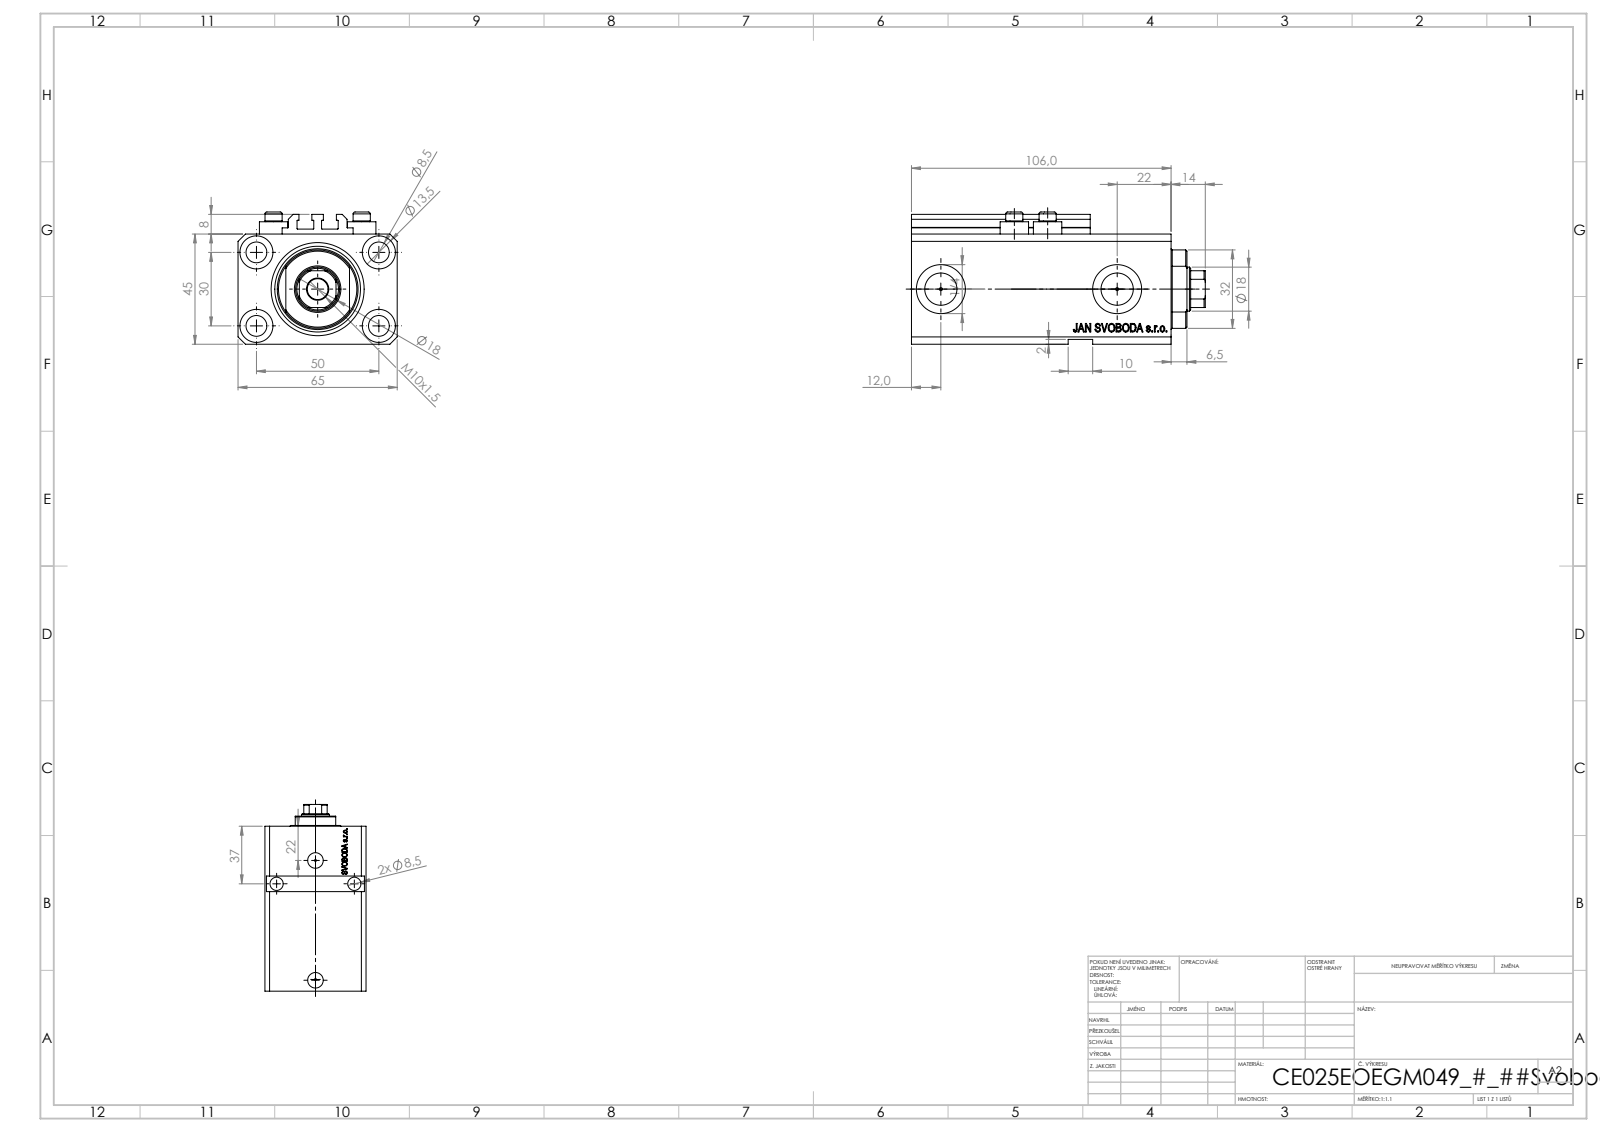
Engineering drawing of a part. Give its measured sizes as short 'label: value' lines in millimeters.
name: V250CE_C_VCP; V250CE_E_Body; ALLEN BOLT V250CE; V250CE_VC_E
written by: SolidWorks 2019 (CONFIG_CONTROL_DESIGN)
unit: mm
bodies: 8 solids, 1067 faces (511 planar, 126 cylindrical, 430 other)
size: 120 × 65 × 54
volume: 274 299 mm³; area: 75 300 mm²
holes: 7× ⌀8.5, 4× ⌀1.25, 4× ⌀4, 4× ⌀13.5, 2× ⌀10, 2× ⌀13.16, 2× ⌀20, 1× ⌀18, 1× ⌀25, 1× ⌀38
bosses: 4× ⌀11.6, 4× ⌀7
rounds: 10× R0.2, 1× R8.5, 1× R16
face distances: 45, 65, 92, 14, 2, 47, 106, 2.5, 10, 20.5
hole spacings: 29.15, 50, 13.6, 15.12, 27.89, 30, 33.62, 36
